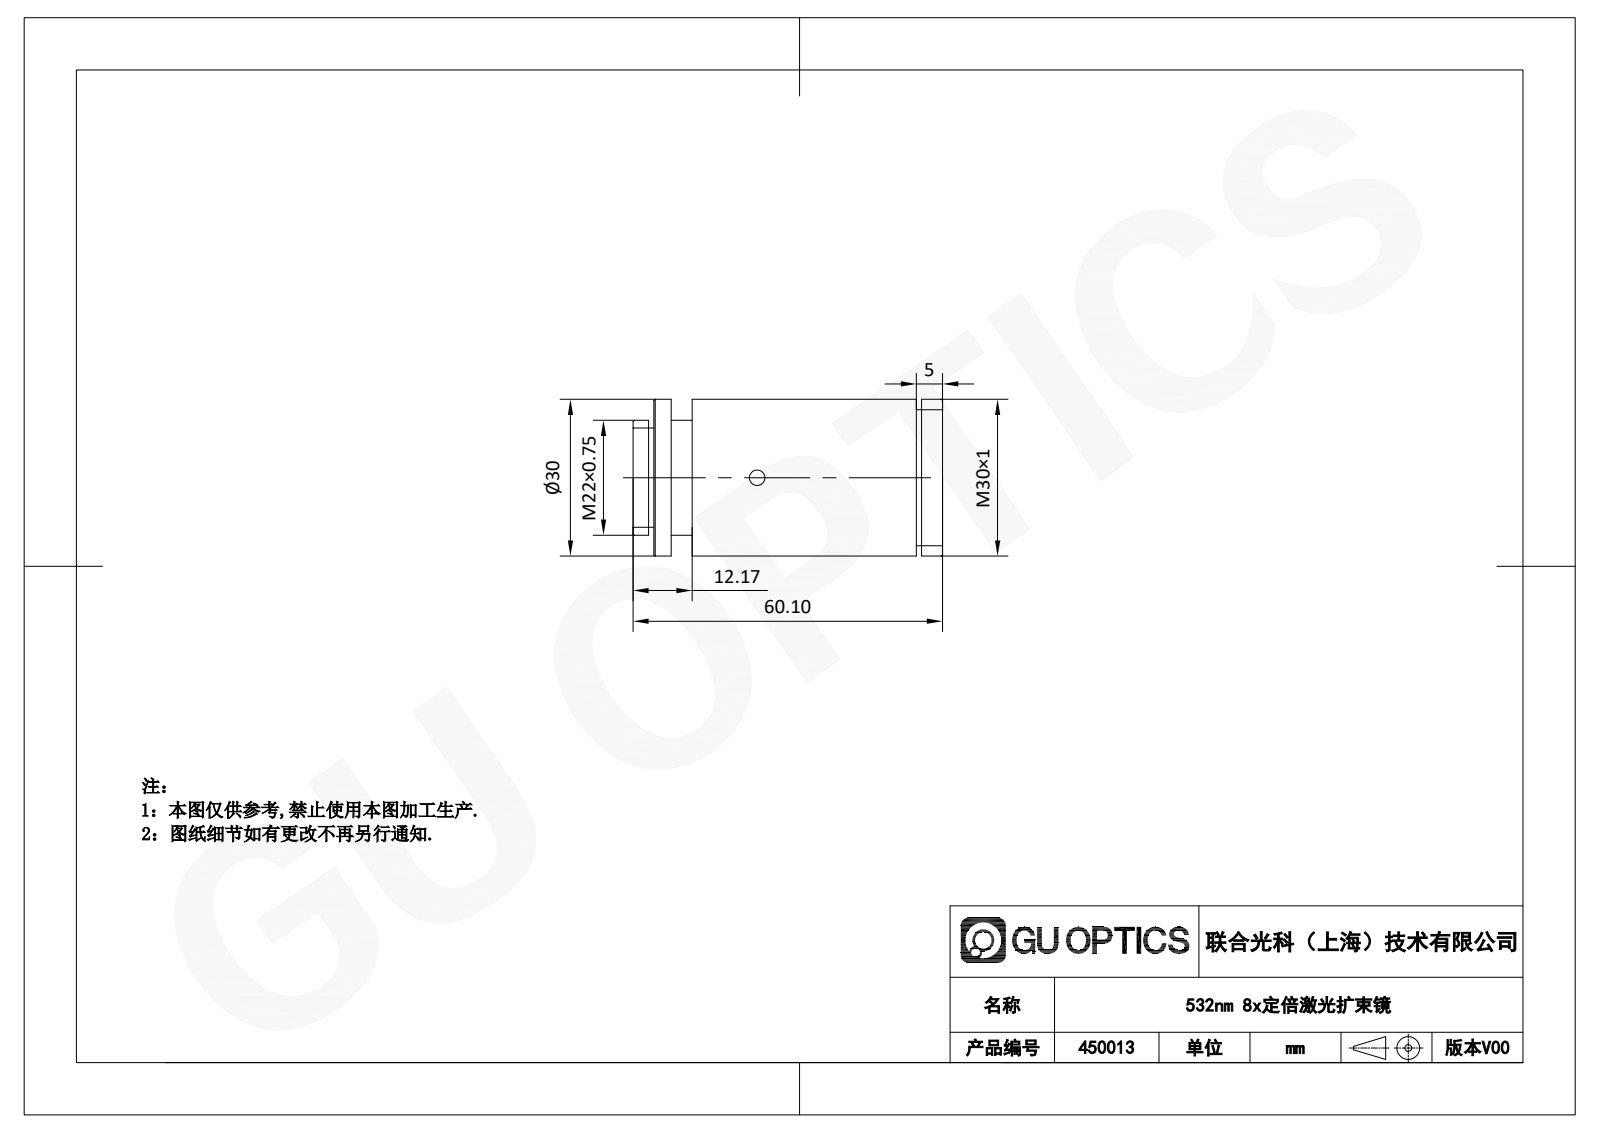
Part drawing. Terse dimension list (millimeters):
name: 450013
written by: SolidWorks 2020 (AUTOMOTIVE_DESIGN)
unit: mm
bodies: 1 solid, 43 faces (11 planar, 22 cylindrical, 10 other)
size: 60.1 × 30 × 30
volume: 32 344 mm³; area: 10 689 mm²
holes: 1× ⌀8, 1× ⌀18
bosses: 1× ⌀30, 1× ⌀26, 1× ⌀22, 1× ⌀19
face distances: 4, 56.1, 47.93, 8.17, 52.1, 4.17, 51.93, 43.93, 1, 12.17
